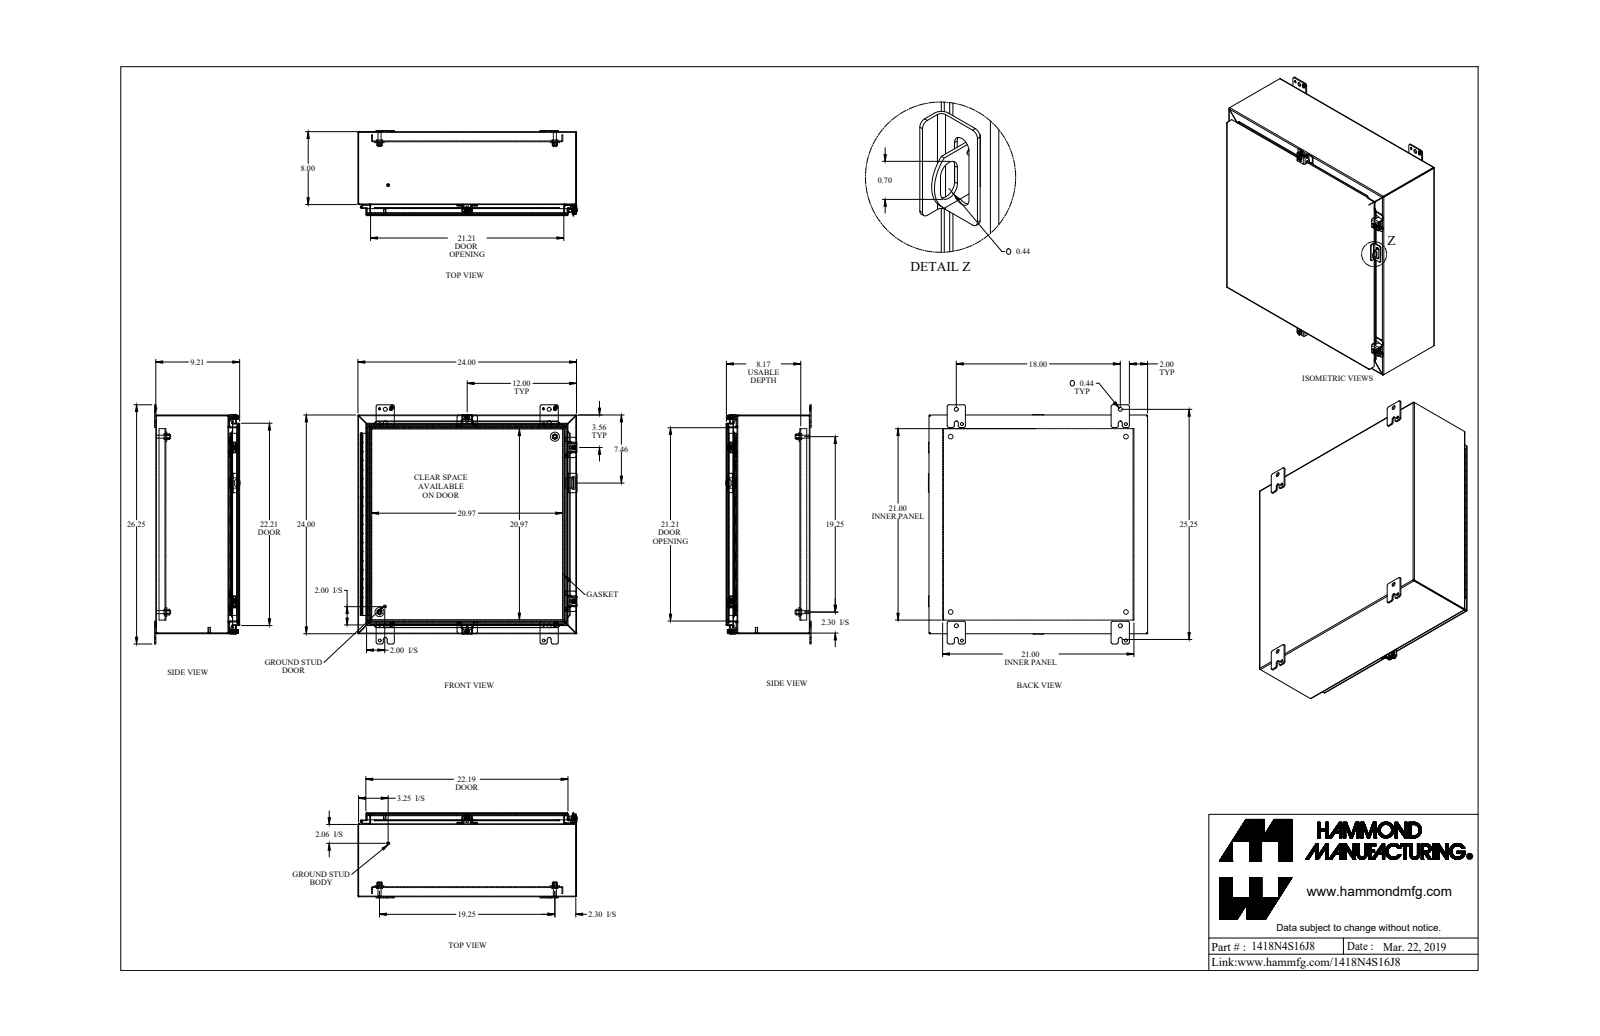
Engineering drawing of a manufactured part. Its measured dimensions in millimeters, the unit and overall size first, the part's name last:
Units: millimetres
Overall size (bounding box): 666.8 × 611.2 × 238.1
Round holes (diameter × count): ⌀5.4 ×4, ⌀6.7 ×4, ⌀8 ×4, ⌀9.5 ×4, ⌀11.1 ×4, ⌀12.7 ×4, ⌀7.8 ×2, ⌀11.3 ×2, ⌀2.8 ×1, ⌀3.2 ×1
Round bosses / shafts (diameter × count): ⌀16.5 ×4, ⌀12.7 ×4, ⌀9.9 ×4, ⌀9.5 ×4, ⌀8.4 ×4, ⌀6.2 ×4, ⌀25.4 ×2, ⌀8 ×2
Partial cylindrical surfaces — rounded edges, fillets, slot ends (radius × count): R4.8 ×26, R0.9 ×24, R2.7 ×24, R1.2 ×21, R3.6 ×21, R6.4 ×20, R3.2 ×12, R1.1 ×8
Main face-to-face distances: 1.8, 607.8, 1.8, 230.3, 232.1, 232.1, 233.9, 23.8, 2.4, 25.6
Hole centre spacings: 489, 250.4, 457.2, 44.1, 595.4, 603.3, 691.5, 756.9
Volume: 3 487 000 mm³ · Surface area: 3 611 000 mm²
Bodies: 39 solids, 1373 faces (746 planar, 493 cylindrical, 134 other)
Part name (STEP PRODUCT): 1418N4S16J8_Default
STEP written by: SolidWorks 2019 (CONFIG_CONTROL_DESIGN)
